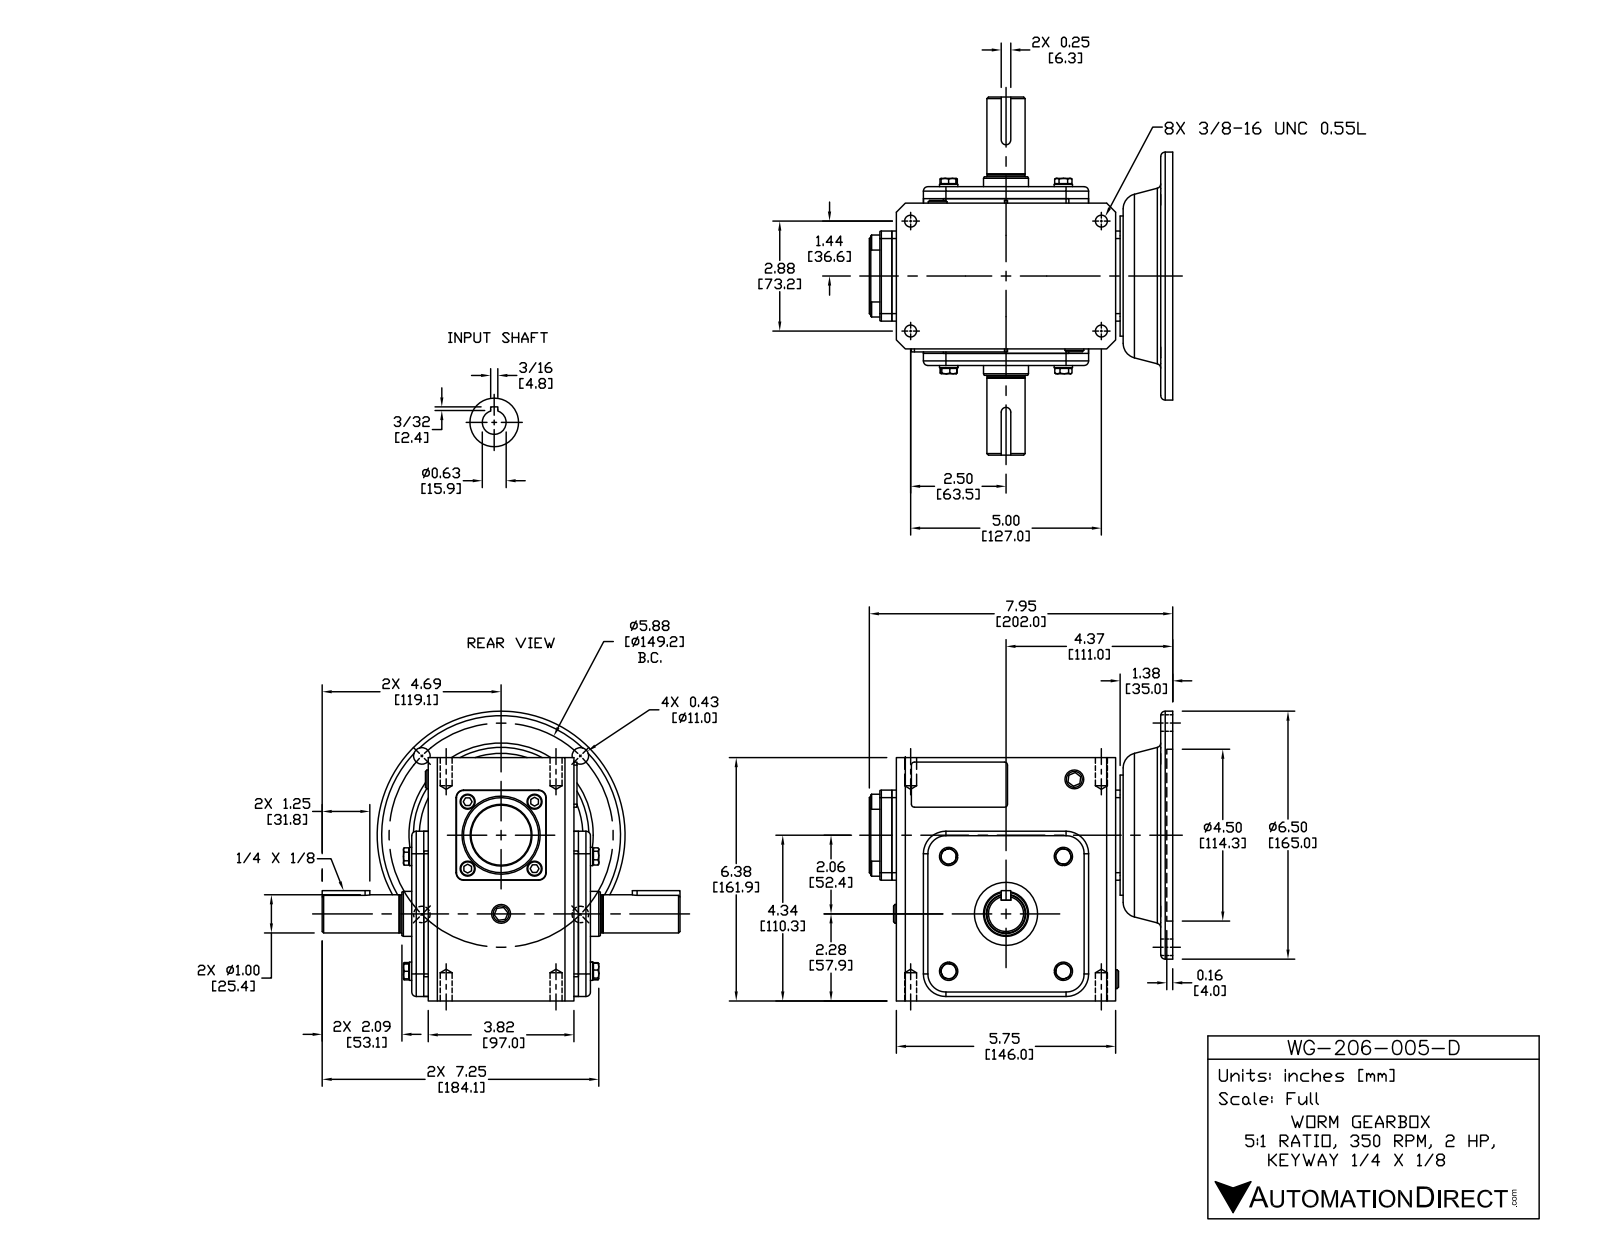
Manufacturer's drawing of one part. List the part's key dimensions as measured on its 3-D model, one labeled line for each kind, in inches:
Part name (STEP PRODUCT): WG-206-005-D
STEP written by: SolidWorks 2015 (CONFIG_CONTROL_DESIGN)
Units: inches
Bodies: 45 solids, 639 faces (311 planar, 194 cylindrical, 134 other)
Overall size (bounding box): 9.38 × 7.953 × 7.591
Volume: 174.7 in³ · Surface area: 422.9 in²
Round holes (diameter × count): ⌀0.313 ×4, ⌀0.406 ×4, ⌀0.591 ×1, ⌀0.625 ×1, ⌀1.181 ×1, ⌀1.457 ×1, ⌀1.654 ×1, ⌀3.543 ×1, ⌀4.5 ×1
Round bosses / shafts (diameter × count): ⌀0.394 ×8, ⌀0.48 ×4, ⌀6.496 ×1, ⌀3.15 ×1, ⌀2.047 ×1, ⌀1.575 ×1, ⌀1.181 ×1, ⌀1.142 ×1
Partial cylindrical surfaces — rounded edges, fillets, slot ends (radius × count): R0.079 ×8, R0.118 ×8, R0.197 ×4, R0.591 ×4, R0.02 ×2, R0.039 ×2, R0.125 ×2, R2.717 ×1
Main face-to-face distances: 0.315, 0.118, 4.055, 0.433, 4.37, 4.252, 3.937, 6.375, 4.685, 0.709
Hole centre spacings: 2.937, 4.154, 2.077, 2.88, 4.631, 5, 5.77, 5.875
